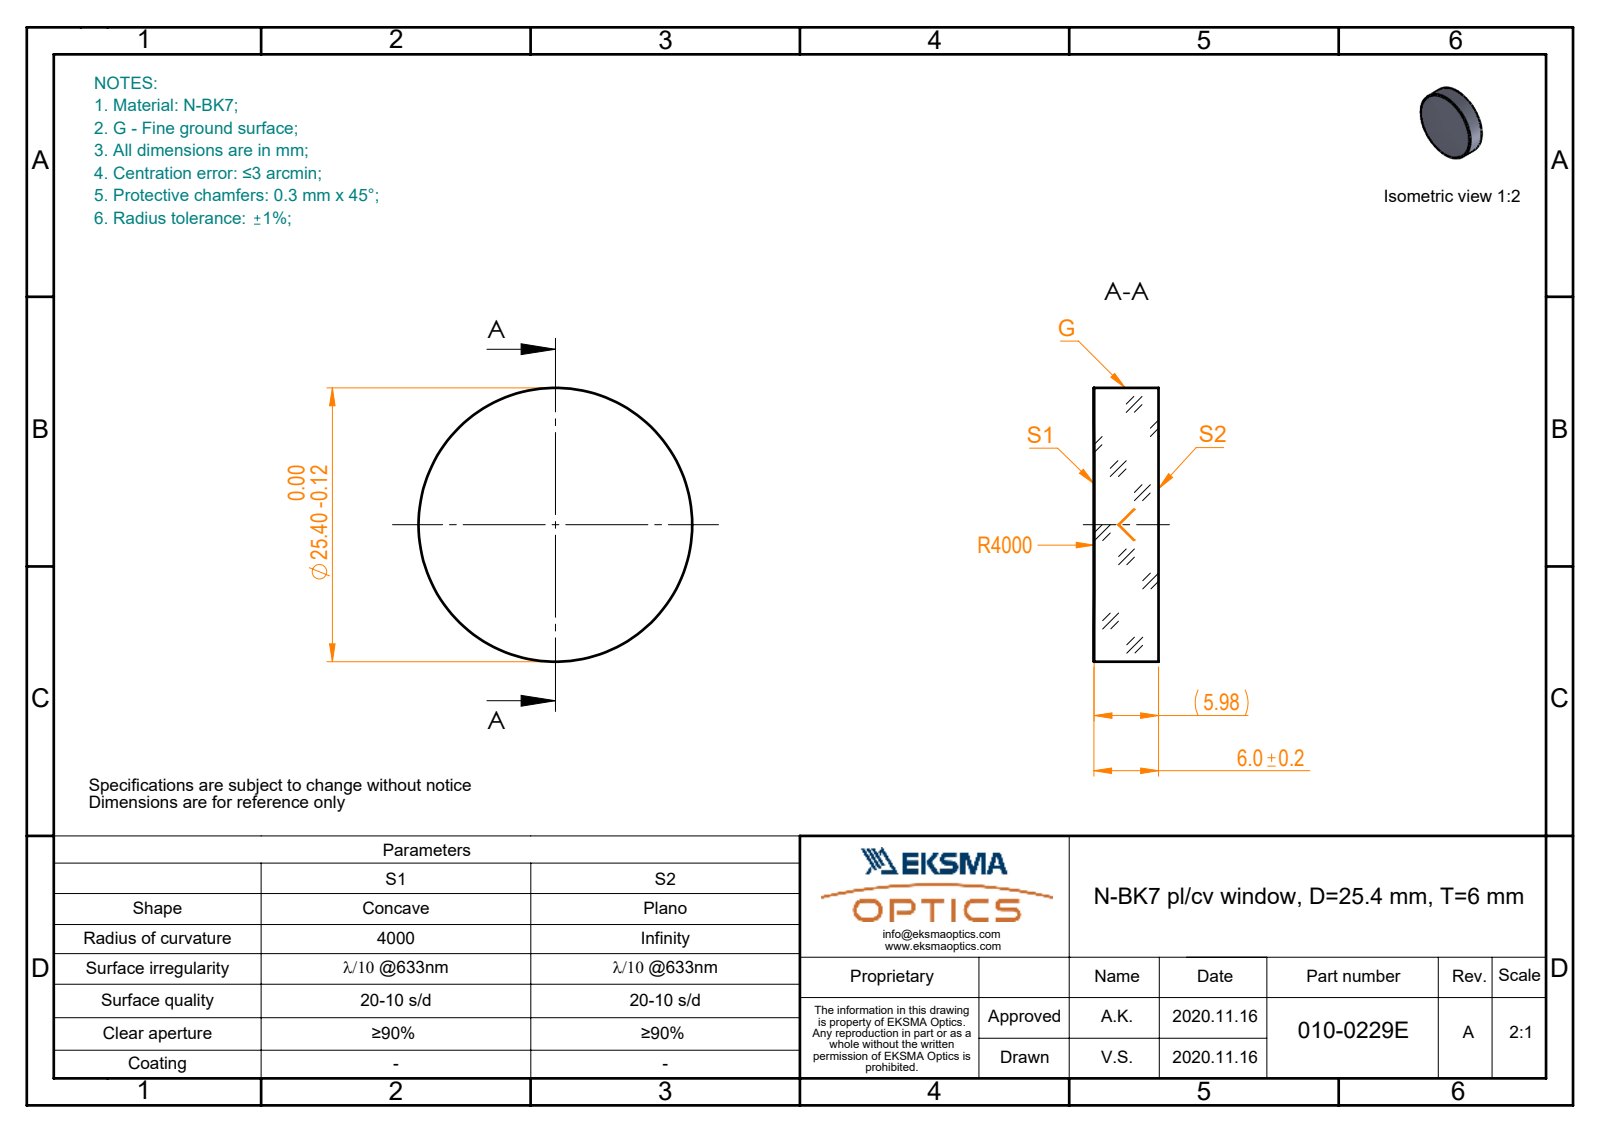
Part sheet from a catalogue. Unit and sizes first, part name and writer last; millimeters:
Units: millimetres
Overall size (bounding box): 25.4 × 25.4 × 6
Round bosses / shafts (diameter × count): ⌀25.4 ×1
Volume: 3 035 mm³ · Surface area: 1 492 mm²
Bodies: 1 solid, 5 faces (1 planar, 2 cylindrical, 2 other)
Part name (STEP PRODUCT): 010-0229E_N-BK7_PCV_window
STEP written by: SolidWorks 2019 (CONFIG_CONTROL_DESIGN)
